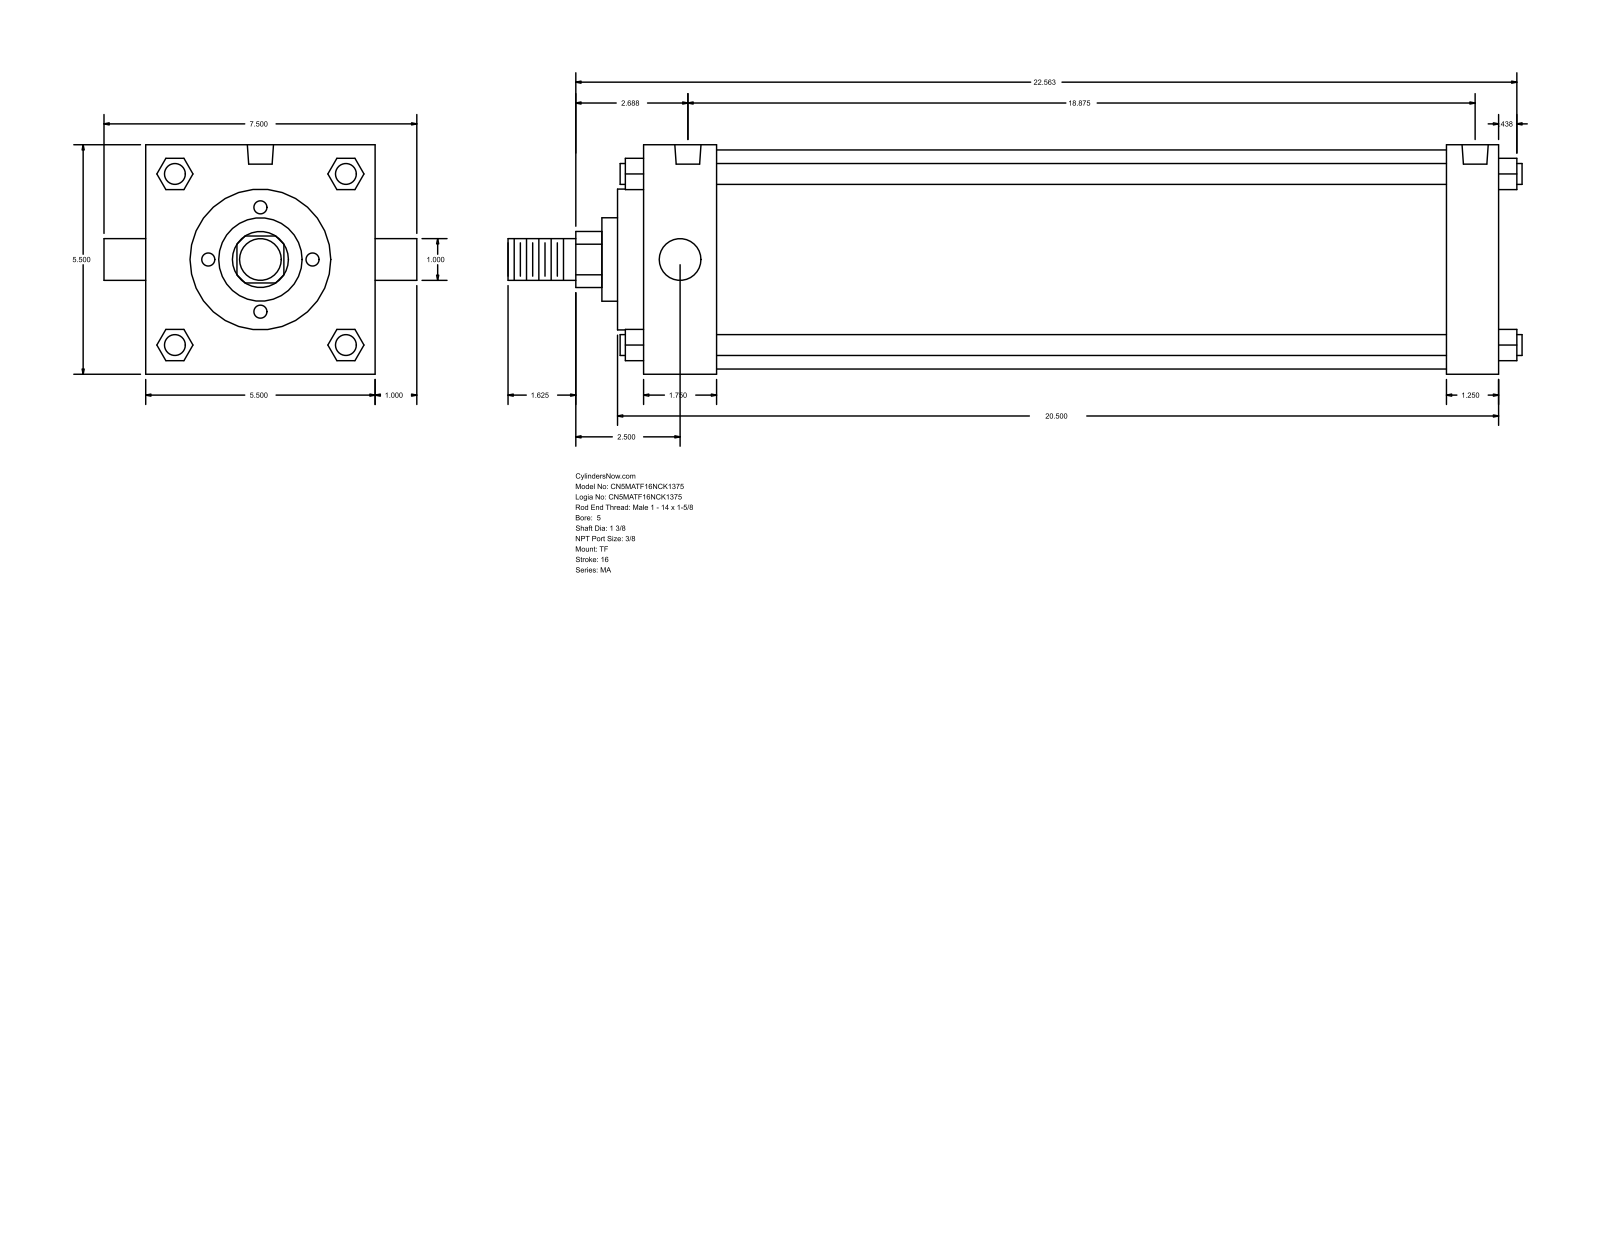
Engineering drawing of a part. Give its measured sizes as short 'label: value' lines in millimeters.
name: MA_TF__0500_1.375
written by: GSSL Pune (CONFIG_CONTROL_DESIGN)
unit: mm
bodies: 0 solids, 122 faces (93 planar, 29 cylindrical, 0 other)
size: 617.54 × 190.5 × 139.7
holes: 3× ⌀11.11, 2× ⌀15.93
bosses: 4× ⌀12.7, 2× ⌀25.4, 1× ⌀133.35, 1× ⌀85.72, 1× ⌀50.8, 1× ⌀34.92
rounds: 1× R17.06
face distances: 139.7, 520.71, 488.96, 31.75, 44.45, 444.51, 476.26, 15.87, 60.32, 504.83
hole spacings: 4.77, 474.66, 469.89, 479.43
